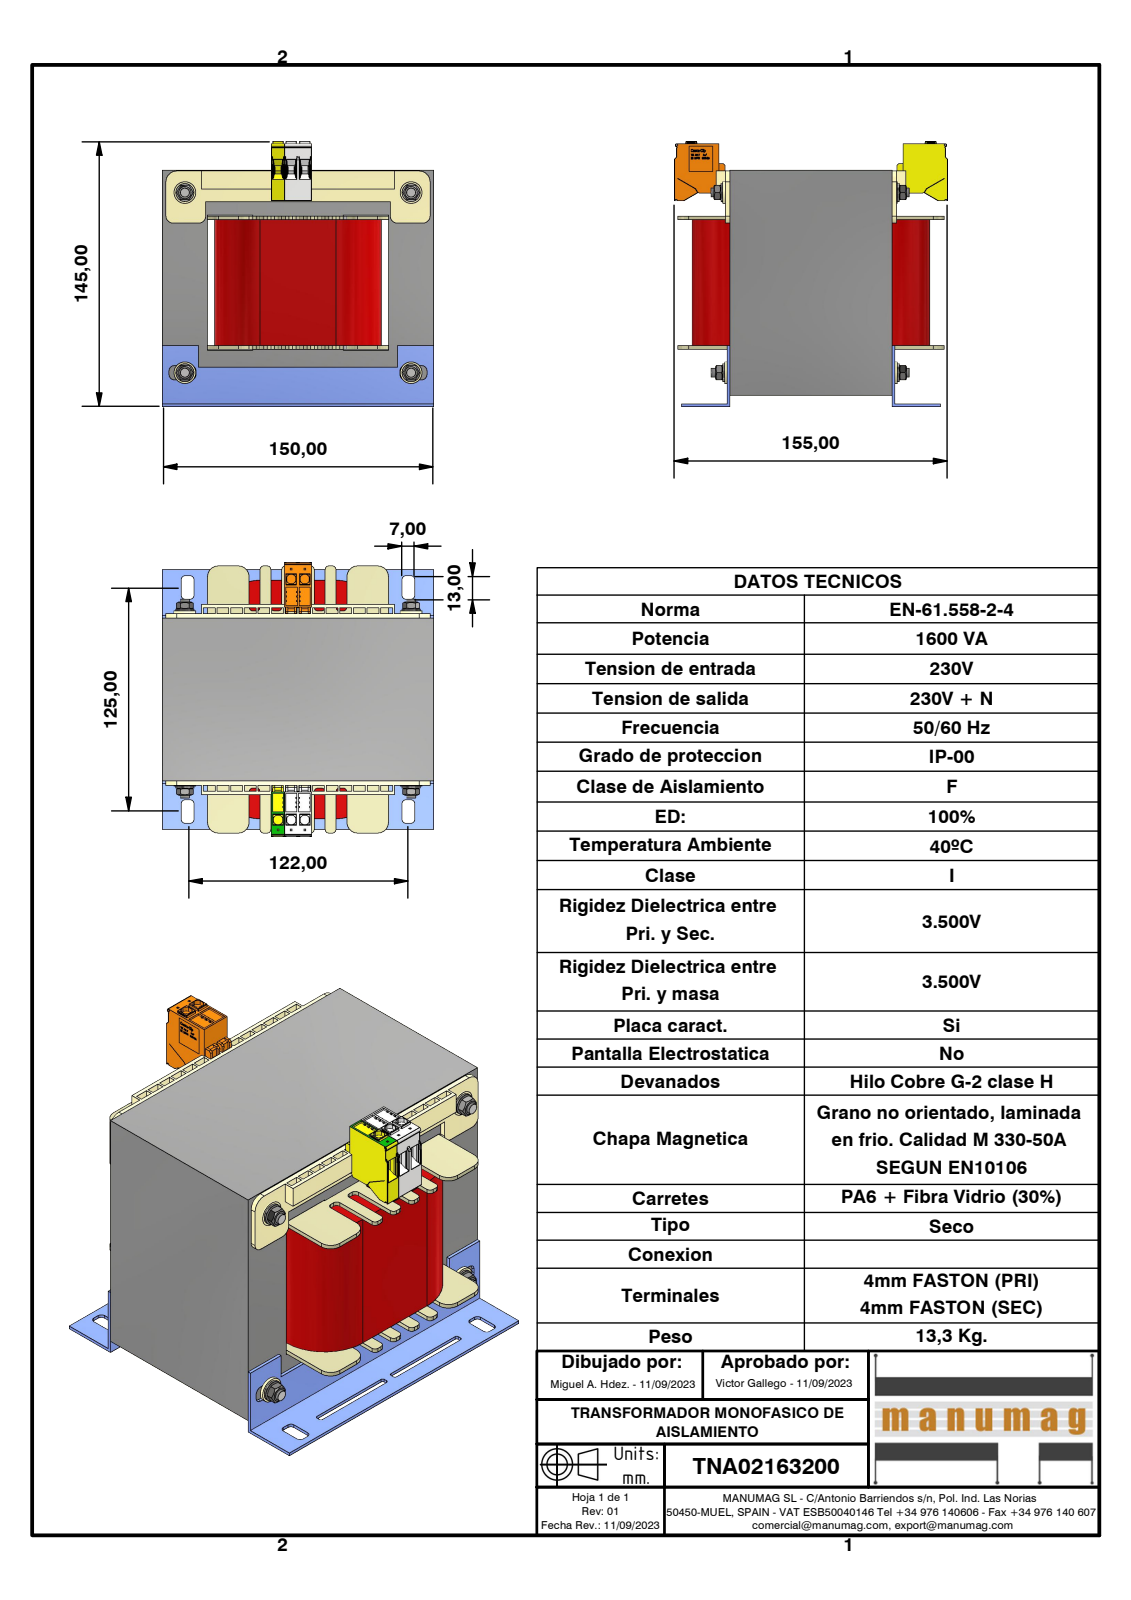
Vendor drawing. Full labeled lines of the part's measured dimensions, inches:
Part name (STEP PRODUCT): TNA02163200; EI150 x 125 - 90 (RC50); AF50DIN; EI 150 X 125 - 90 (+8 more)
STEP written by: Autodesk Inventor 2023 (AUTOMOTIVE_DESIGN)
Units: inches
Bodies: 37 solids, 5349 faces (4383 planar, 678 cylindrical, 288 other)
Overall size (bounding box): 5.98 × 5.906 × 5.803
Volume: 118.2 in³ · Surface area: 437.1 in²
Round holes (diameter × count): ⌀0.163 ×4, ⌀0.197 ×4, ⌀0.209 ×4, ⌀0.315 ×4
Round bosses / shafts (diameter × count): ⌀0.472 ×4, ⌀0.394 ×4, ⌀0.232 ×4
Partial cylindrical surfaces — rounded edges, fillets, slot ends (radius × count): R0.006 ×216, R0.008 ×70, R0.079 ×52, R0.039 ×24, R0.02 ×18, R0.012 ×12, R0.236 ×10, R0.118 ×8
Main face-to-face distances: 0.984, 3.937, 1.969, 4.921, 3.543, 2.953, 3.917, 1.004, 0.827, 0.059
Hole centre spacings: 3.937, 4.921, 6.302
